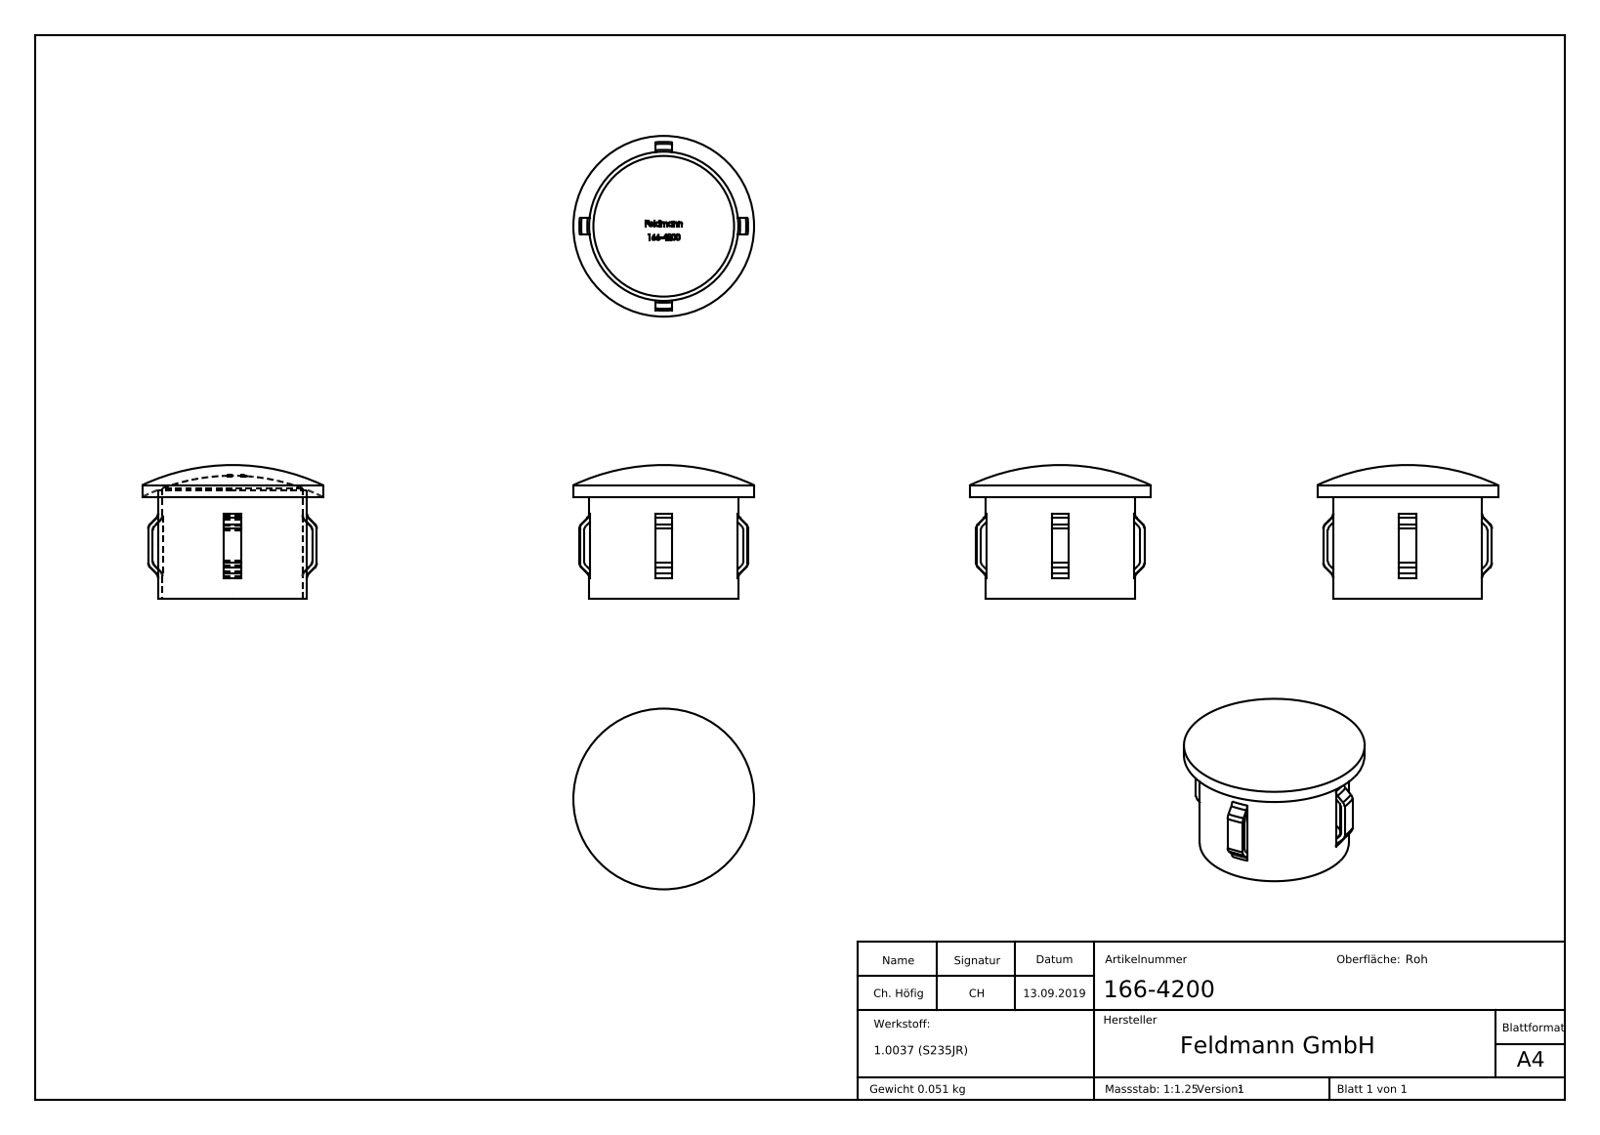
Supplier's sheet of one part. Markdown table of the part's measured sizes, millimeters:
| quantity | value |
| --- | --- |
| part name | 166-4200 |
| STEP written by | SolidWorks 2015 (CONFIG_CONTROL_DESIGN) |
| units | millimeters |
| bodies | 1 solid, 311 faces (106 planar, 16 cylindrical, 189 other) |
| overall size | 42.4 × 42.4 × 31.4 |
| volume | 6 495 mm³ |
| surface area | 9 106 mm² |
| round holes (diameter × count) | 33 × 1 |
| round bosses / shafts (diameter × count) | 42.4 × 1, 35 × 1 |
| partial cylindrical surfaces (radius × count) | 18.8 × 1, 19.8 × 1 |
| main face-to-face distances | 4, 2, 2.97, 2.85, 0.39, 1.26, 1.41, 3.66, 3.88, 3.27 |
